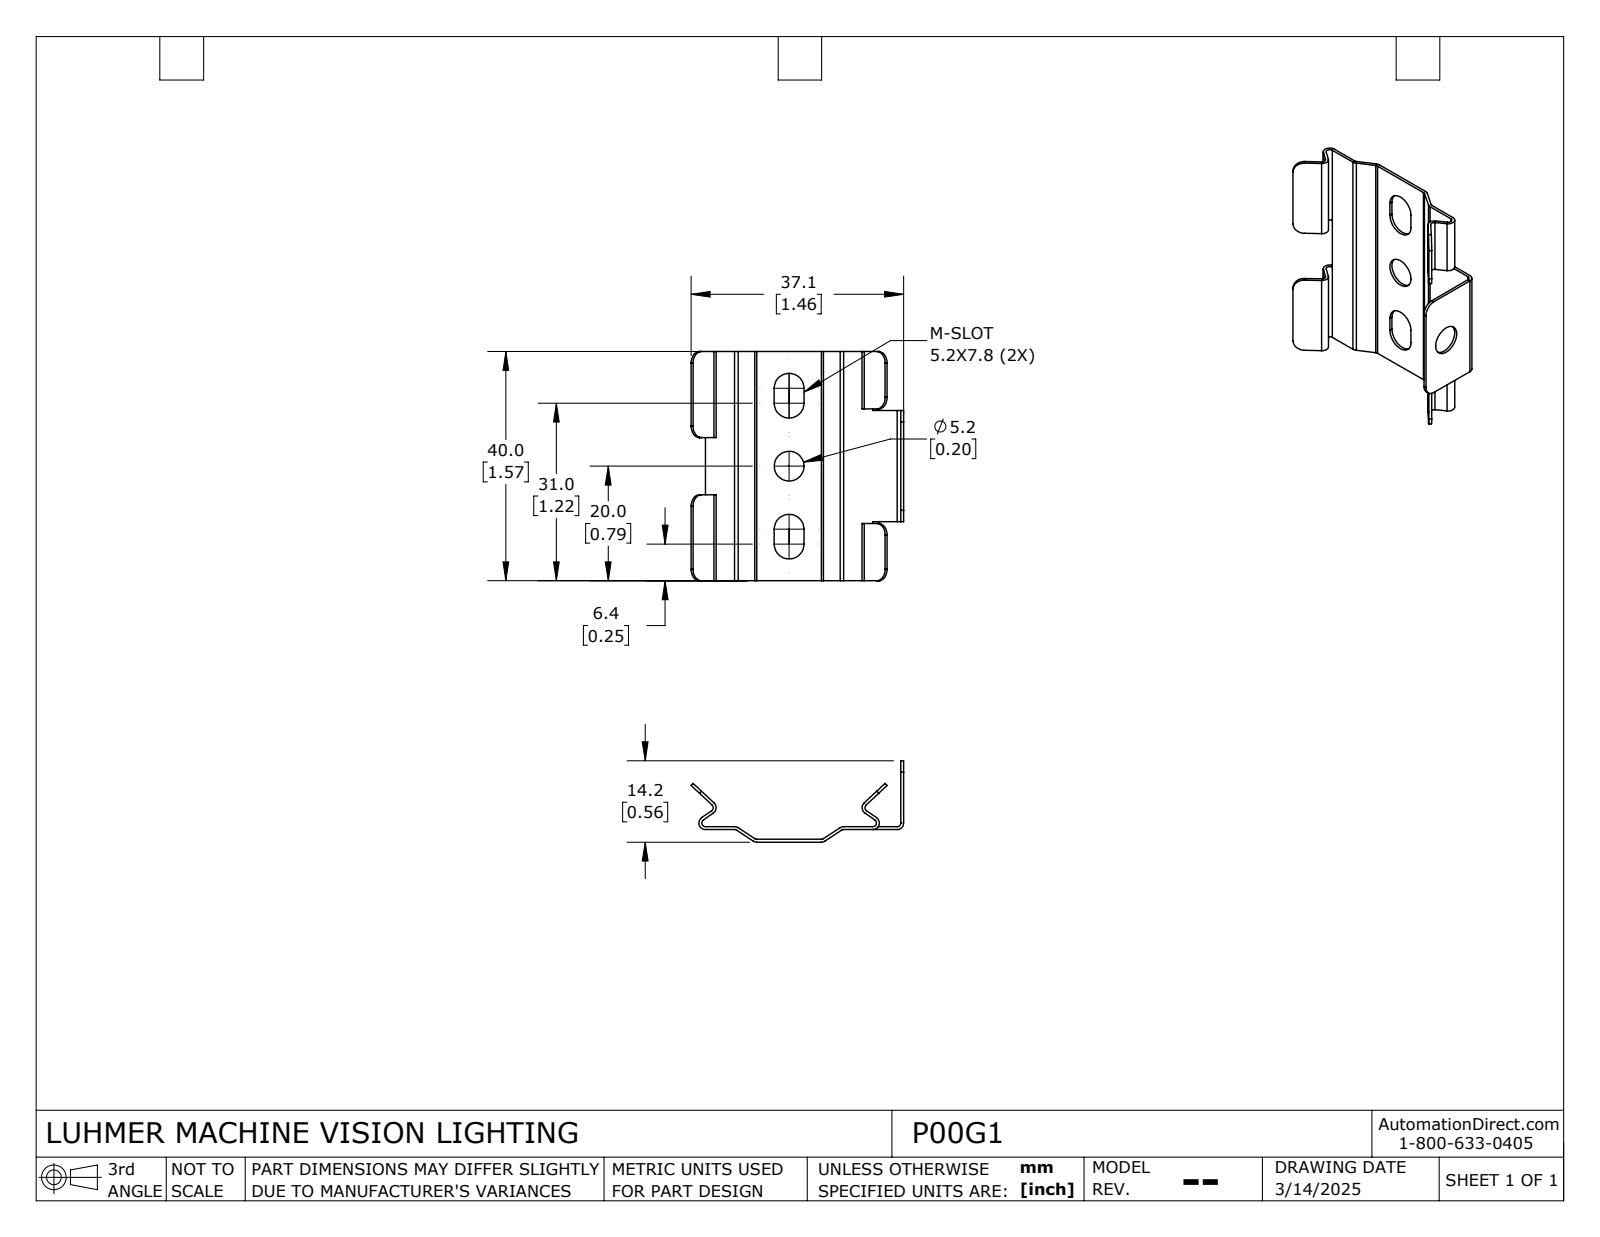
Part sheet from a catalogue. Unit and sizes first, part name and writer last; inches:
Units: inches
Overall size (bounding box): 1.575 × 1.461 × 0.559
Round holes (diameter × count): ⌀0.205 ×2
Partial cylindrical surfaces — rounded edges, fillets, slot ends (radius × count): R0.079 ×10, R0.025 ×9, R0.045 ×9, R0.102 ×4
Main face-to-face distances: 0.02, 0.087, 0.106, 0.067, 0.02, 1.575, 0.591, 0.406, 1.169, 0.394
Volume: 0.06 in³ · Surface area: 6.353 in²
Bodies: 1 solid, 91 faces (49 planar, 42 cylindrical, 0 other)
Part name (STEP PRODUCT): P00G1
STEP written by: SolidWorks 2017 (CONFIG_CONTROL_DESIGN)
